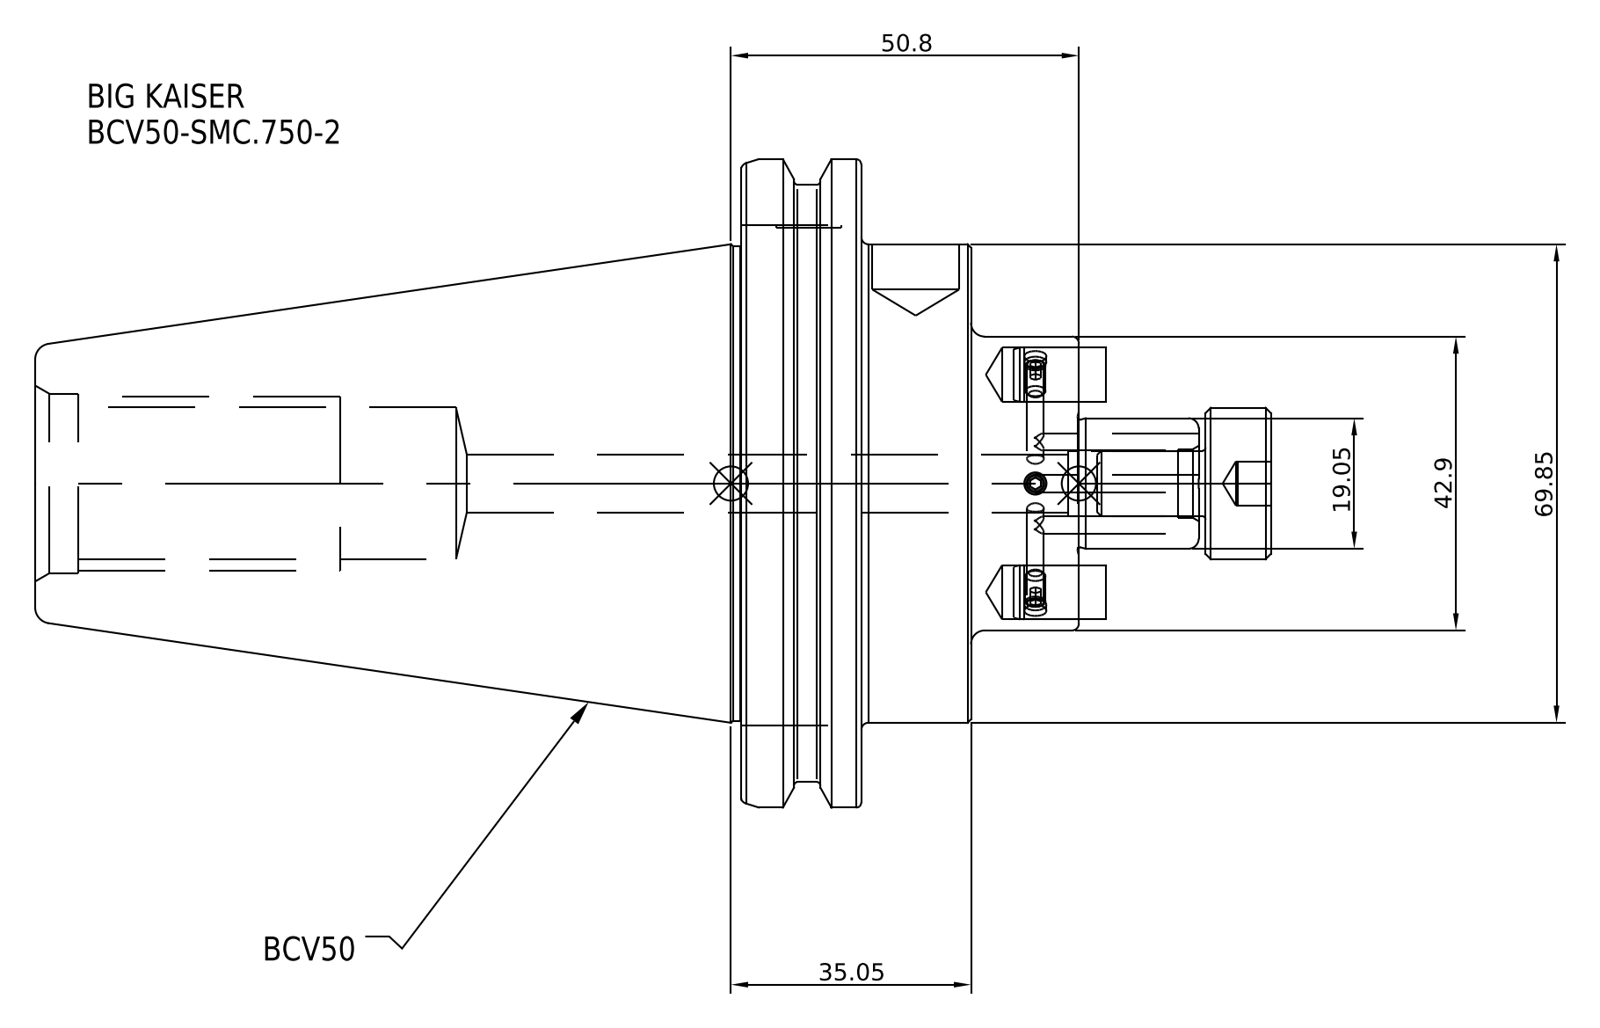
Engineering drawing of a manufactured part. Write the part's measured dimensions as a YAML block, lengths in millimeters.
part_name: "BCV50-SMC_750-2"
step_written_by: "SolidWorks 2021 (CONFIG_CONTROL_DESIGN)"
units: millimeters
bodies: {solids: 1, faces: 38, planar: 18, cylindrical: 14, other: 6}
overall_size: [156.36, 98.43, 98.43]
volume: 465059
surface_area: 43775
round_holes:
  - {diameter: 8.43, count: 1}
round_bosses_or_shafts:
  - {diameter: 98.43, count: 1}
  - {diameter: 91.29, count: 1}
  - {diameter: 69.85, count: 1}
  - {diameter: 42.9, count: 1}
face_to_face_distances: [17.55, 16, 33.55, 31.75, 136.65, 120.65, 103.1, 15.75, 49.3, 152.4]
